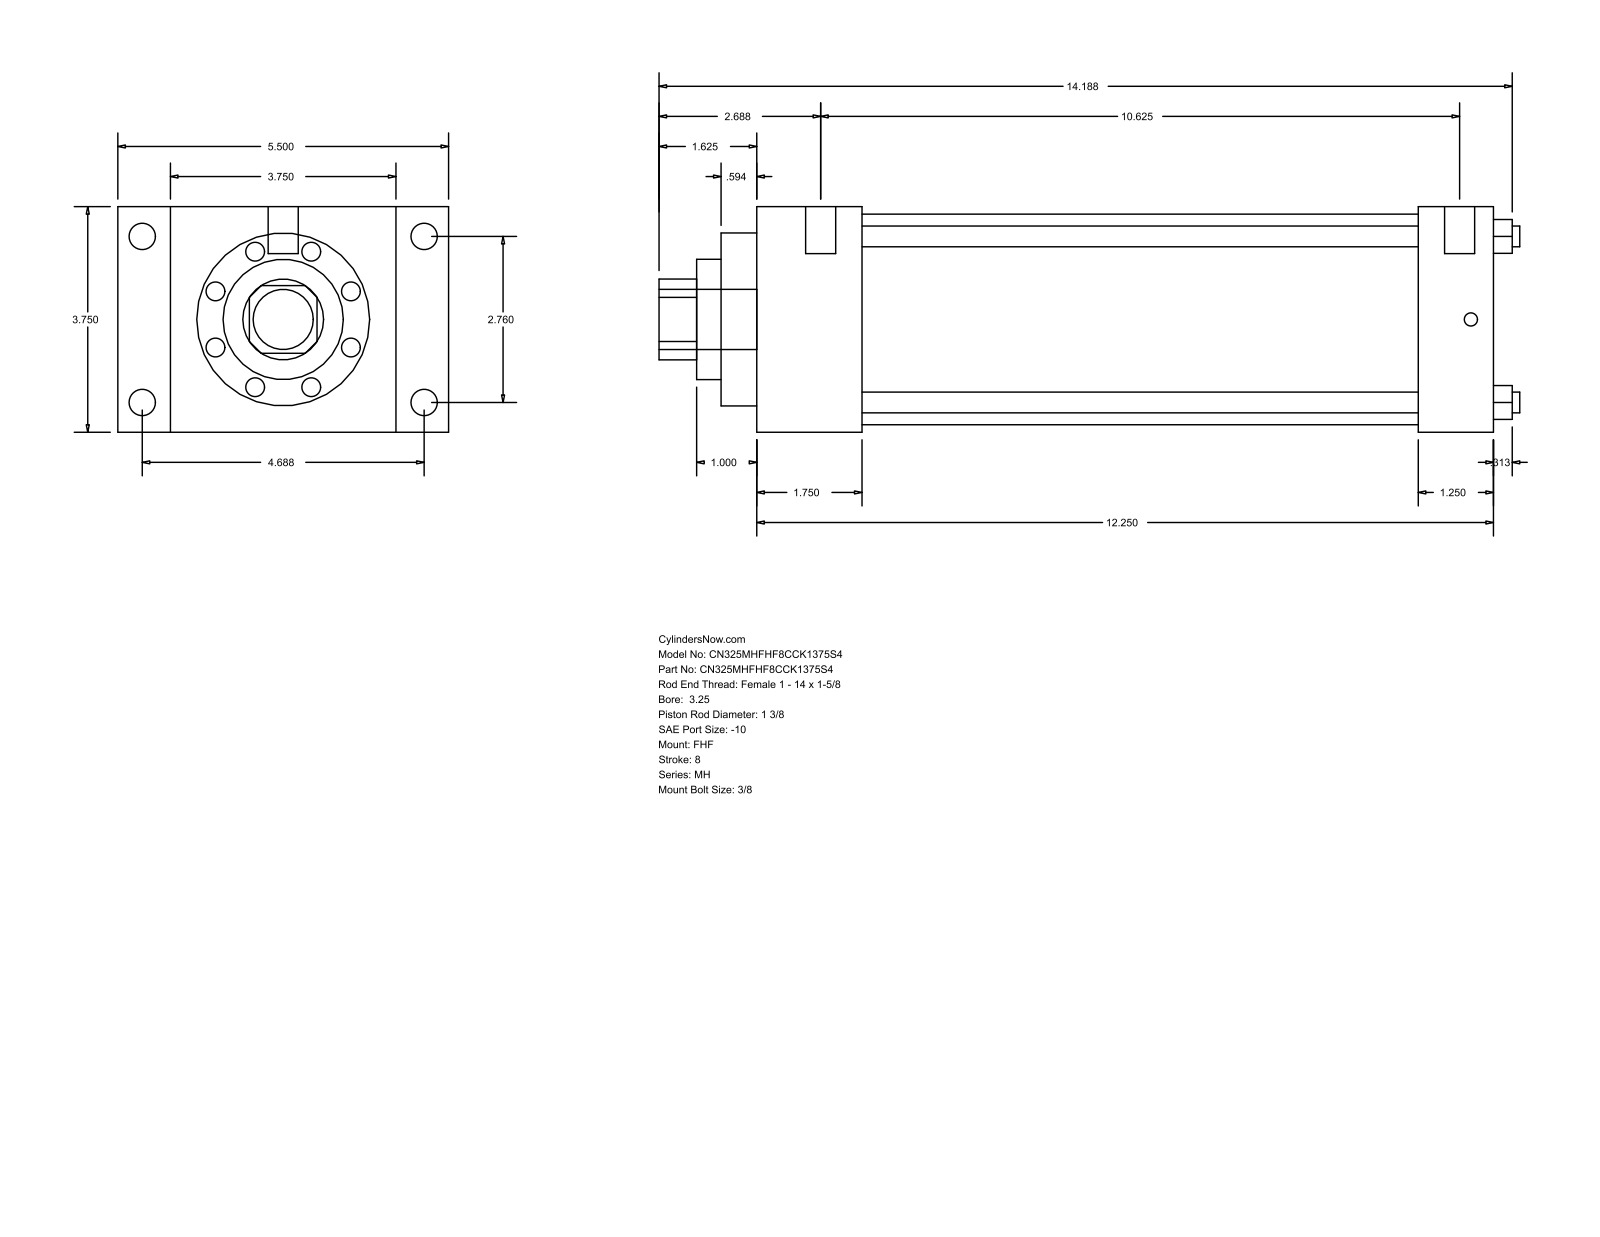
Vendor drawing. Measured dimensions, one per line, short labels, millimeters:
name: MH_FHF__0325_1.375
written by: GSSL Pune (CONFIG_CONTROL_DESIGN)
unit: mm
bodies: 0 solids, 90 faces (61 planar, 29 cylindrical, 0 other)
size: 363.54 × 139.7 × 95.25
holes: 4× ⌀8.76, 1× ⌀34.92, 1× ⌀50.8, 1× ⌀73.03, 1× ⌀88.9
bosses: 4× ⌀11.13, 4× ⌀5.56, 2× ⌀12.7, 1× ⌀25.4
rounds: 1× R17.06
face distances: 95.24, 311.16, 44.45, 266.71, 22.23, 117.47, 139.7, 279.41, 234.96, 31.75
hole spacings: 49.57, 70.1, 99.14
